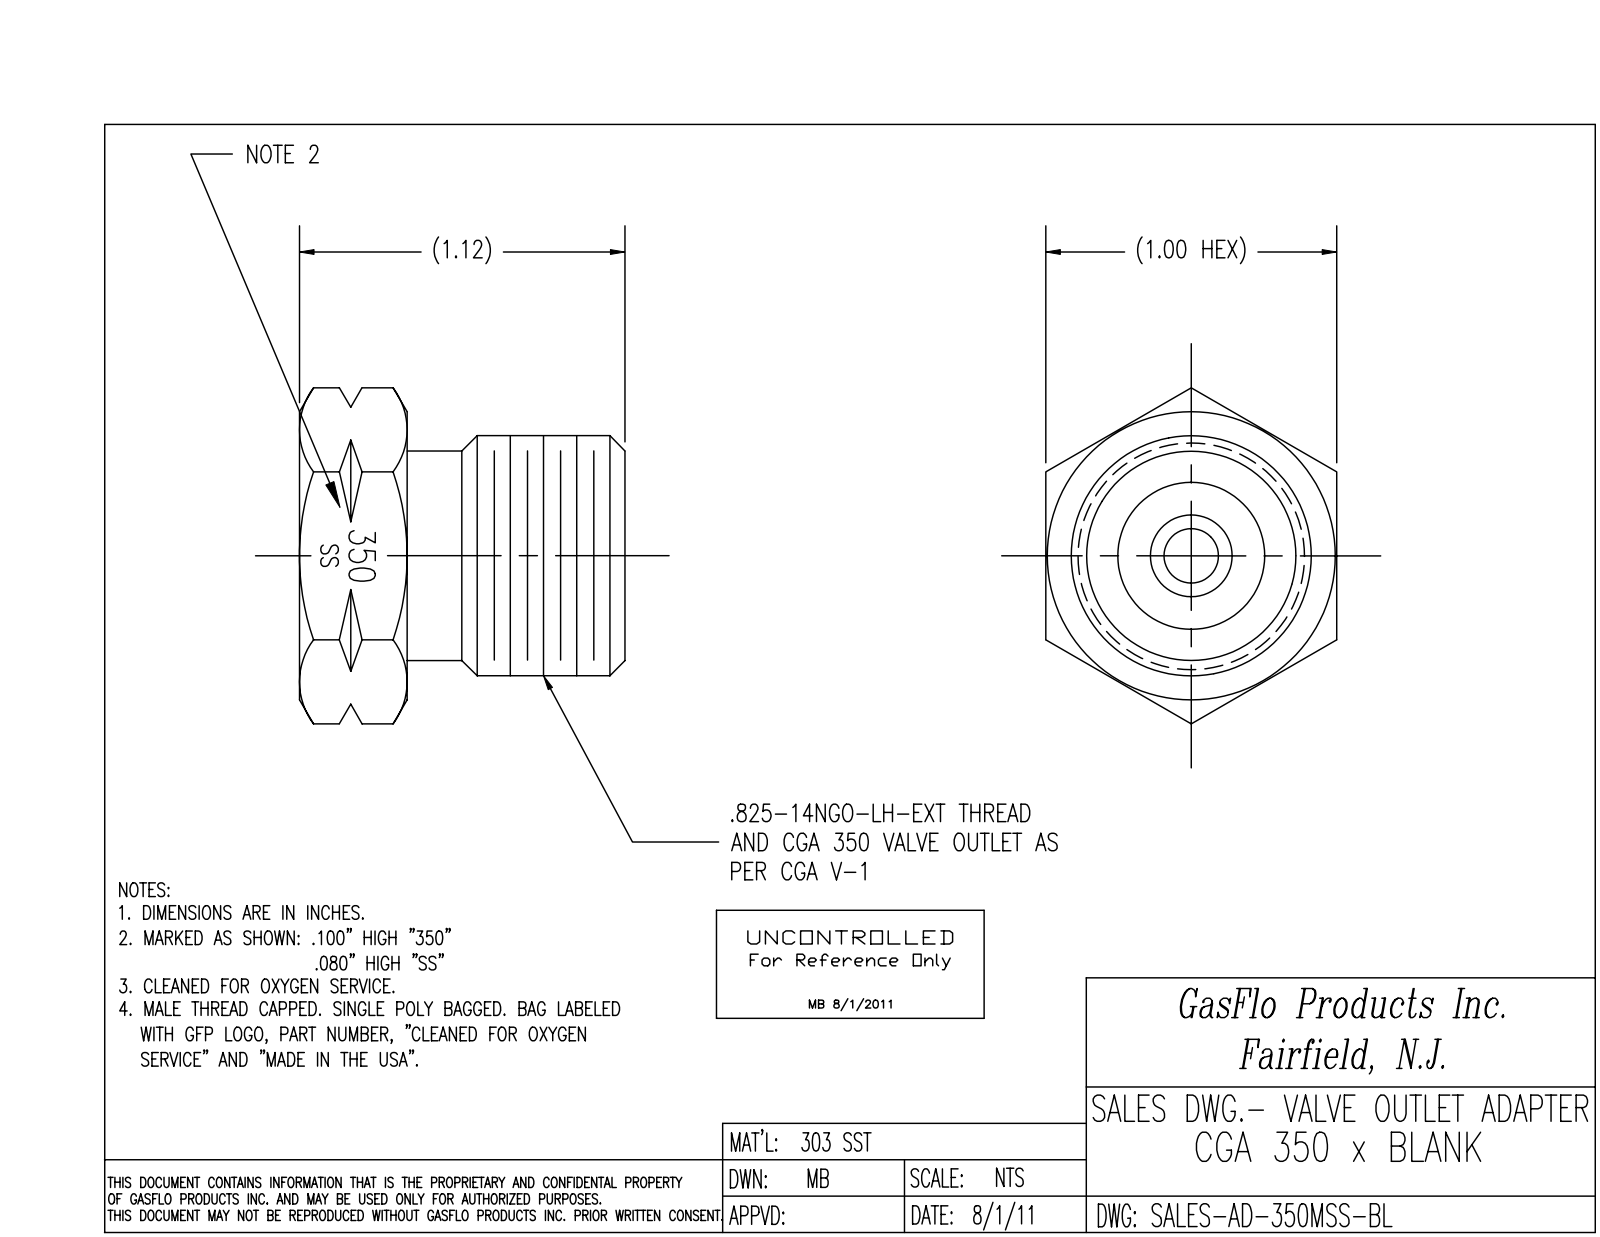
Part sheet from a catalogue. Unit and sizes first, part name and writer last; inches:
Units: inches
Overall size (bounding box): 1.155 × 1.12 × 1
Round holes (diameter × count): ⌀0.281 ×1, ⌀0.505 ×1
Round bosses / shafts (diameter × count): ⌀0.823 ×1, ⌀0.723 ×1, ⌀0.72 ×1
Main face-to-face distances: 1, 0.37, 1.12, 0.75, 0.995, 0.324, 0.046, 0.796, 0.314, 0.056
Volume: 0.564 in³ · Surface area: 6.341 in²
Bodies: 1 solid, 157 faces (28 planar, 35 cylindrical, 94 other)
Part name (STEP PRODUCT): AD-350MSS-BL
STEP written by: SolidWorks 2018 (CONFIG_CONTROL_DESIGN)
